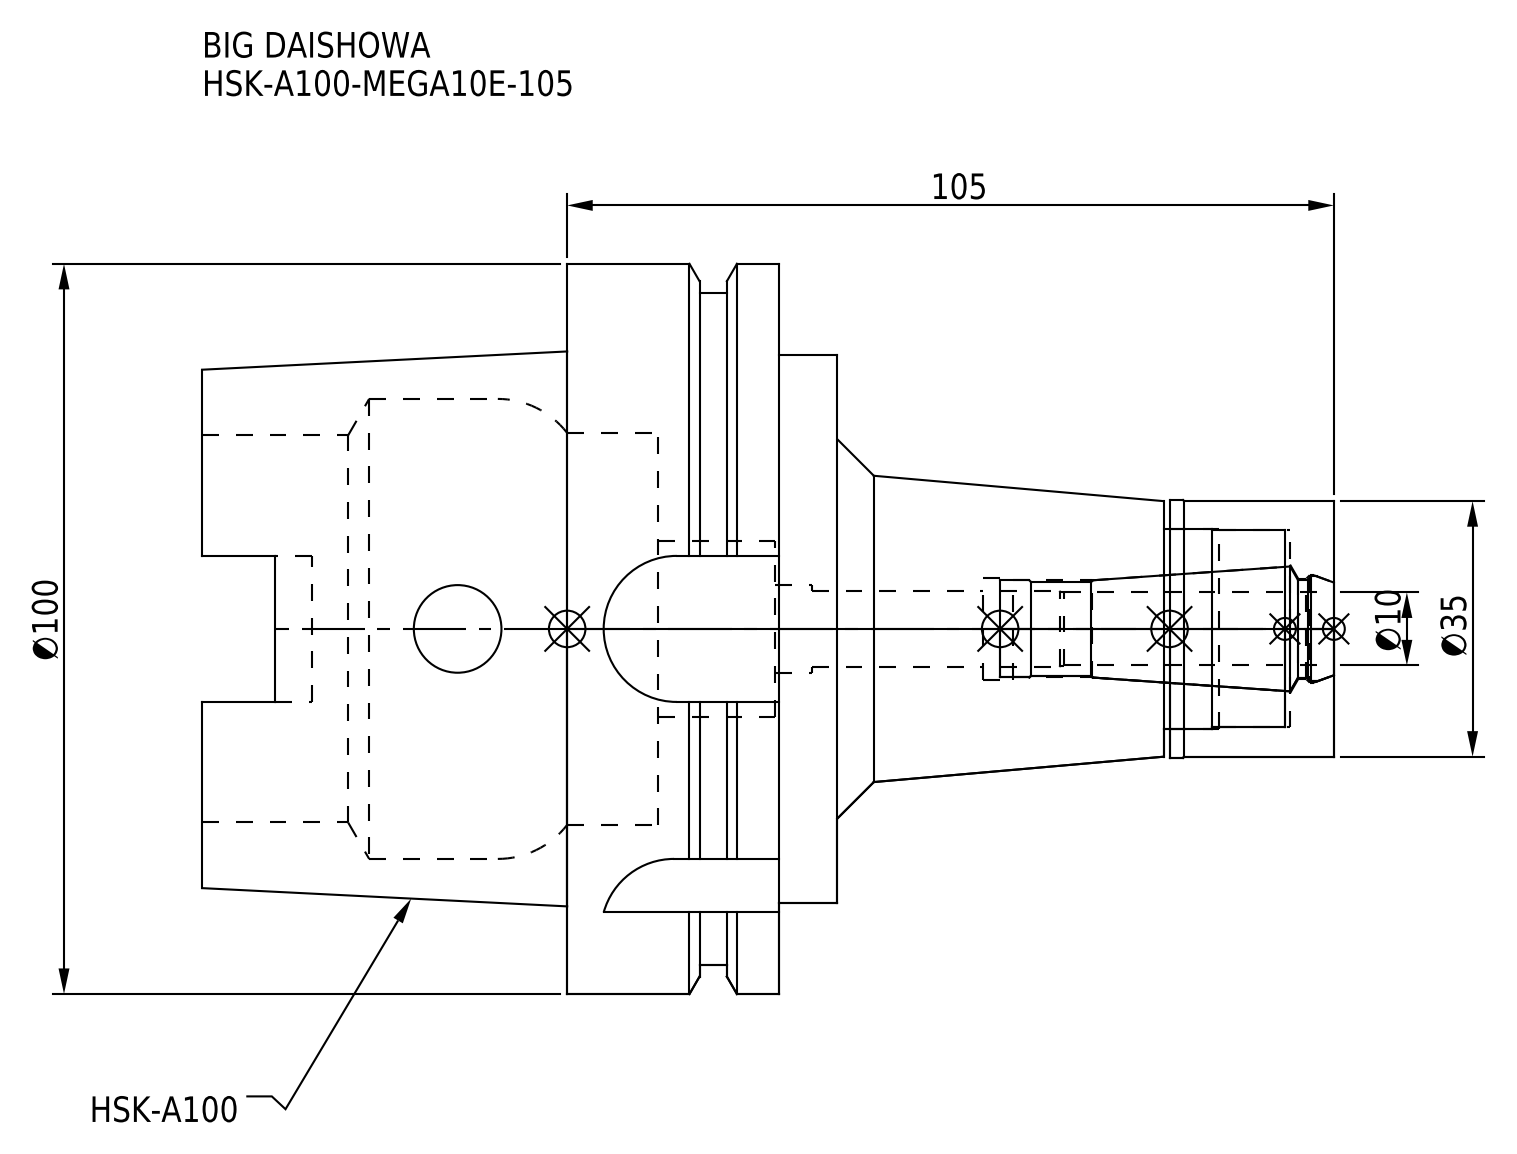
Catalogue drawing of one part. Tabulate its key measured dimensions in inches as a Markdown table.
| quantity | value |
| --- | --- |
| part name | DXF_TEMP_ASSY_ASM_4_ASM.stp; HA100ME10105-100_ASM.stp; HSK-A100-MEGA10E-105_1.stp; MEN10_1.stp (+3 more) |
| STEP written by | SolidWorks 2019 (CONFIG_CONTROL_DESIGN) |
| units | inches |
| bodies | 2 solids, 126 faces (42 planar, 56 cylindrical, 28 other) |
| overall size | 6.102 × 3.937 × 3.937 |
| volume | 21.68 in³ |
| surface area | 103 in² |
| round holes (diameter × count) | 0.472 × 2, 0.409 × 1, 0.524 × 1, 0.543 × 1, 0.547 × 1, 0.579 × 1, 0.945 × 1, 1.063 × 1, 1.083 × 1, 2.087 × 1, 2.118 × 1, 2.48 × 1 |
| round bosses / shafts (diameter × count) | 3.937 × 1, 3.622 × 1, 2.953 × 1, 1.39 × 1, 1.378 × 1 |
| partial cylindrical surfaces (radius × count) | 0.192 × 4, 0.394 × 4 |
| main face-to-face distances | 1.142, 0.315, 1.457, 0.967, 0.652, 0.49, 3.425, 3.11, 2.459, 1.969 |
